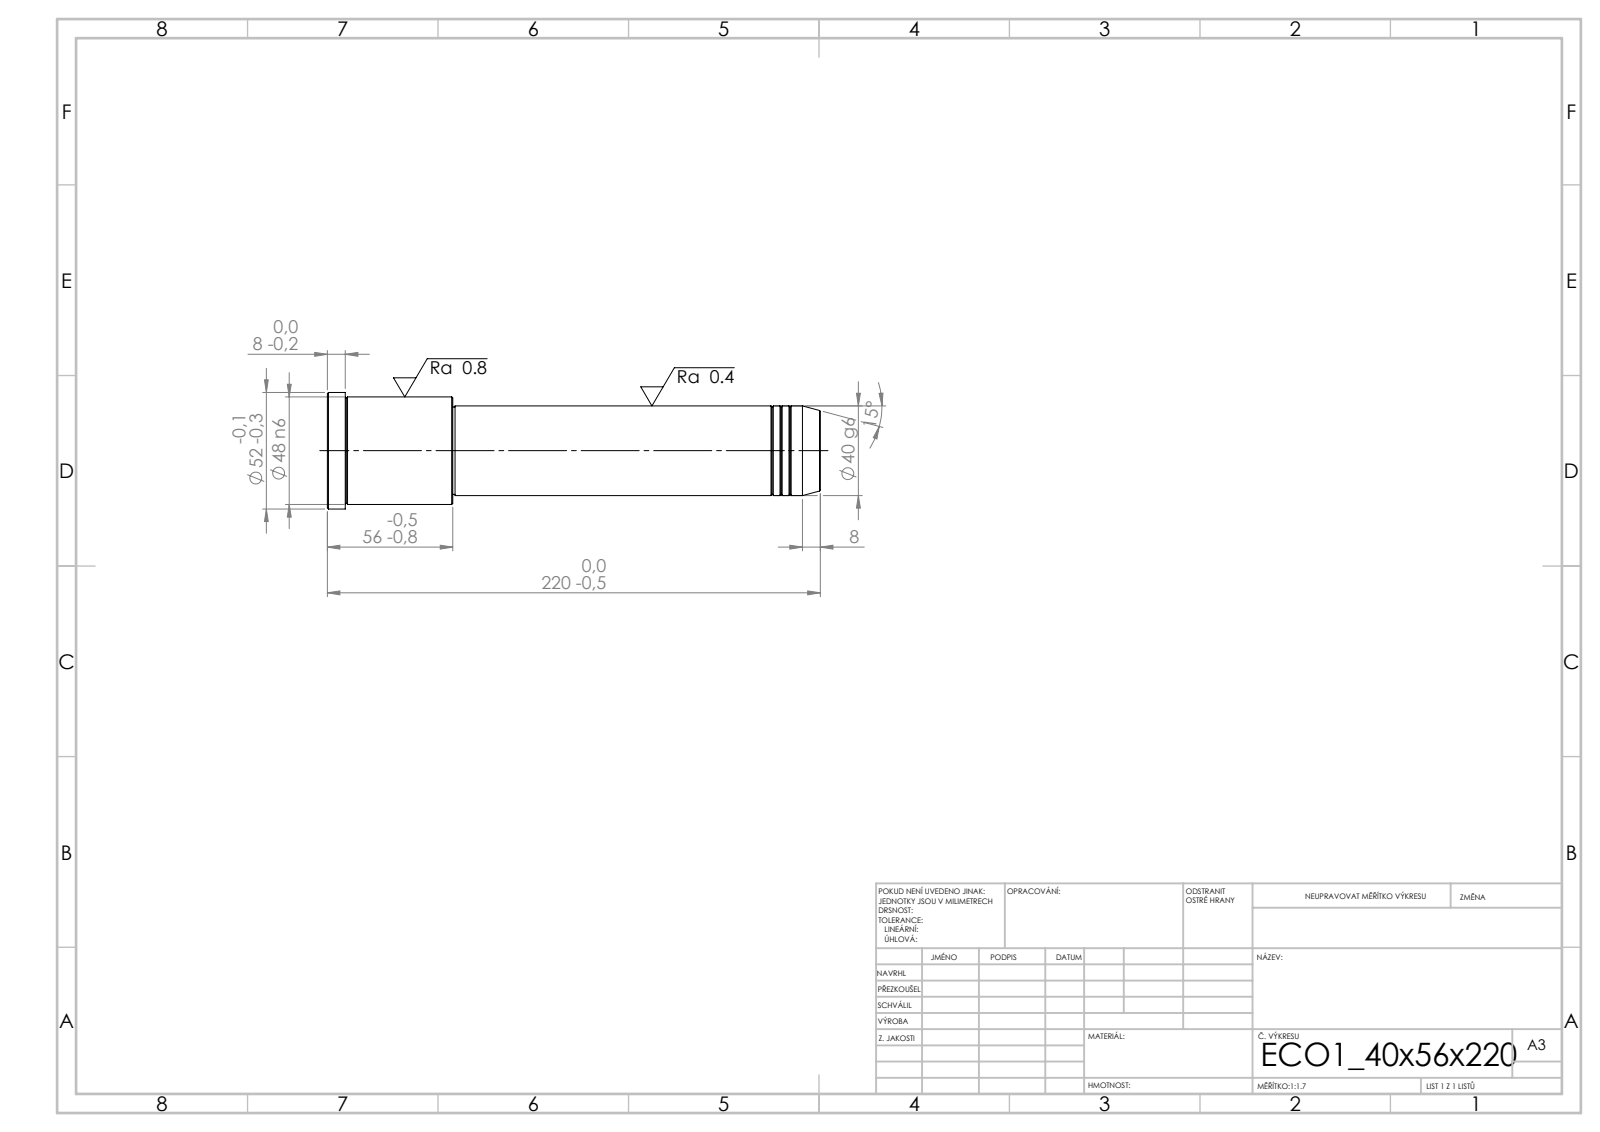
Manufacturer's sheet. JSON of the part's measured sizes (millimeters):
{"step_written_by": "SolidWorks 2019 (CONFIG_CONTROL_DESIGN)", "units": "millimeters", "bodies": {"solids": 1, "faces": 43, "planar": 5, "cylindrical": 14, "other": 24}, "overall_size": [220, 52, 52], "volume_mm3": 308589, "surface_area_mm2": 33430, "round_bosses_or_shafts": [[52, 1], [48, 1], [40, 1], [39, 1]], "face_to_face_distances": [220, 164, 56, 212, 48, 8, 163, 1, 49, 57]}
